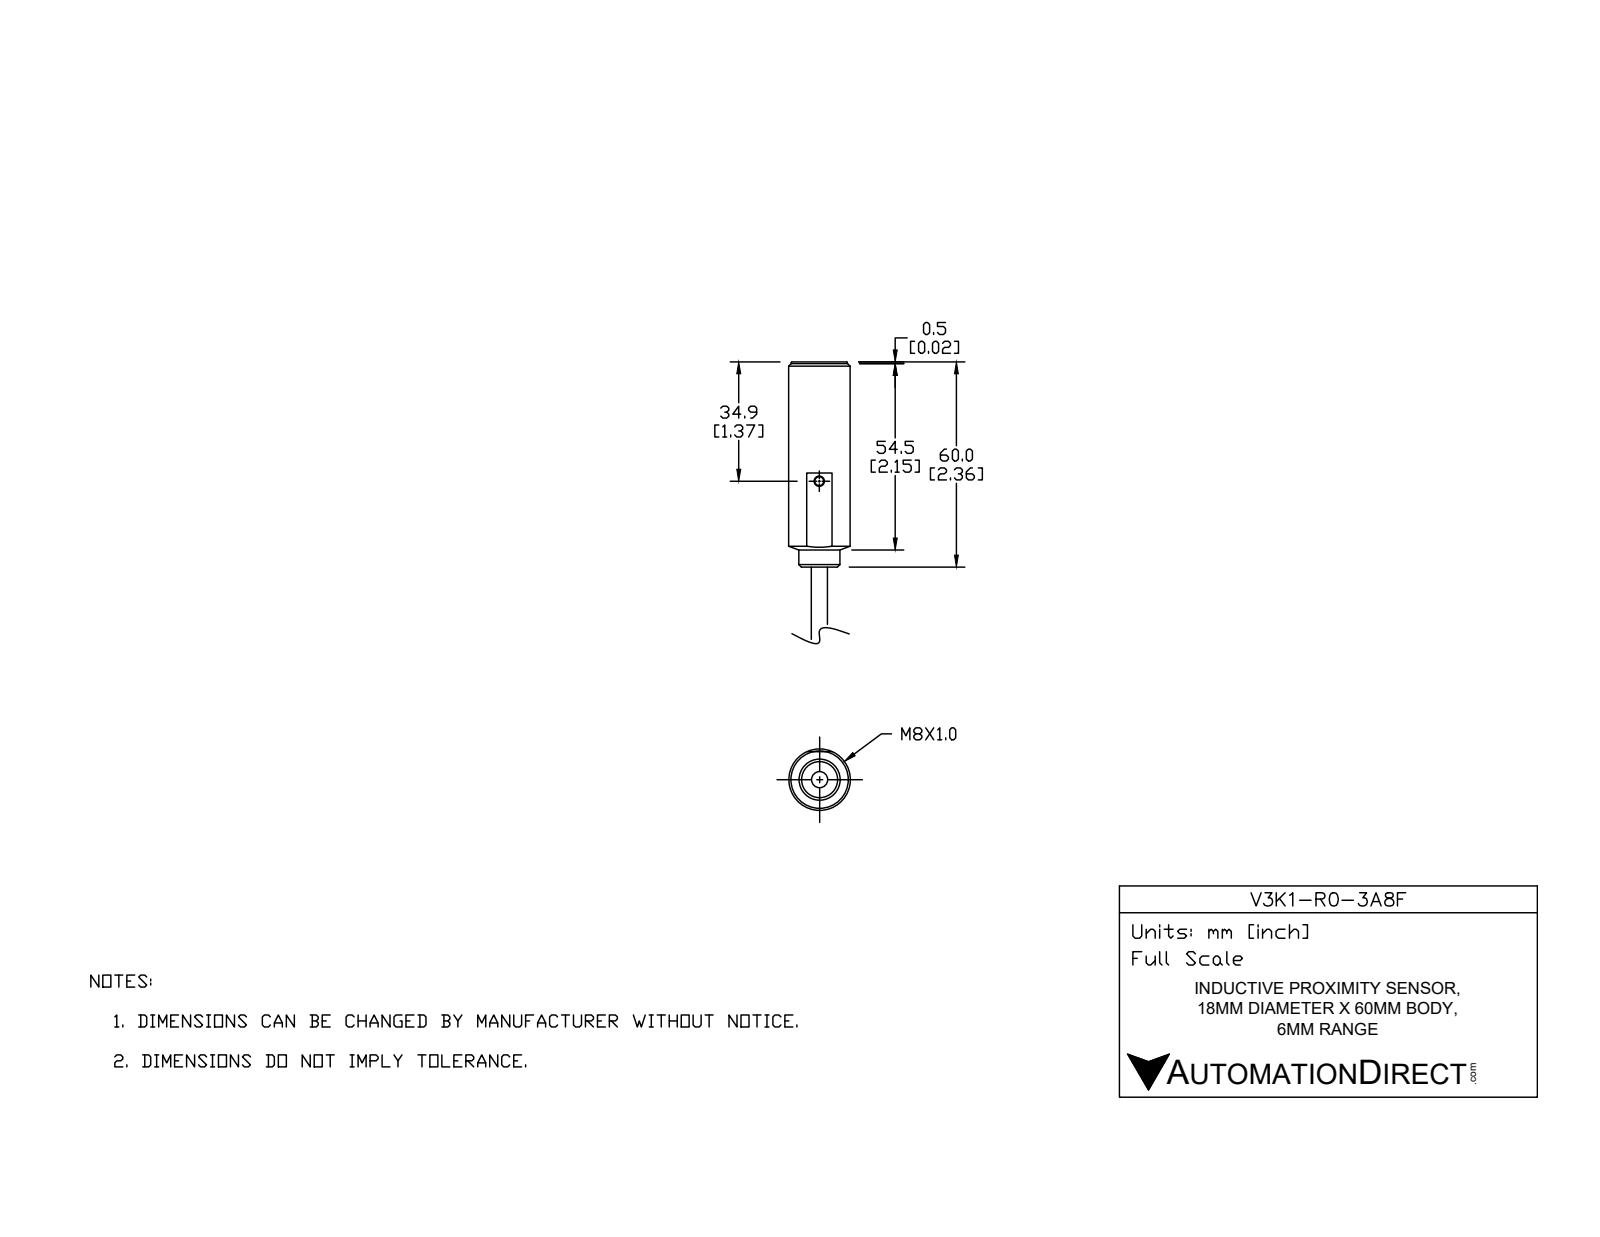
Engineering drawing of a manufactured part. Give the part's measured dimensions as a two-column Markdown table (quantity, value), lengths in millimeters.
| quantity | value |
| --- | --- |
| part name | V3K1_3A_fig |
| STEP written by | ST-DEVELOPER v16.7 (AUTOMOTIVE_DESIGN) |
| units | millimeters |
| bodies | 1 solid, 17 faces (7 planar, 5 cylindrical, 5 other) |
| overall size | 100 × 18 × 18 |
| volume | 15 033 mm³ |
| surface area | 4 301 mm² |
| round holes (diameter × count) | 2.6 × 1 |
| round bosses / shafts (diameter × count) | 18 × 1, 16.4 × 1, 12 × 1, 4.7 × 1 |
| main face-to-face distances | 60, 100, 40, 1.2, 32.5, 27.5, 67.5, 0.5, 32, 59.5 |
